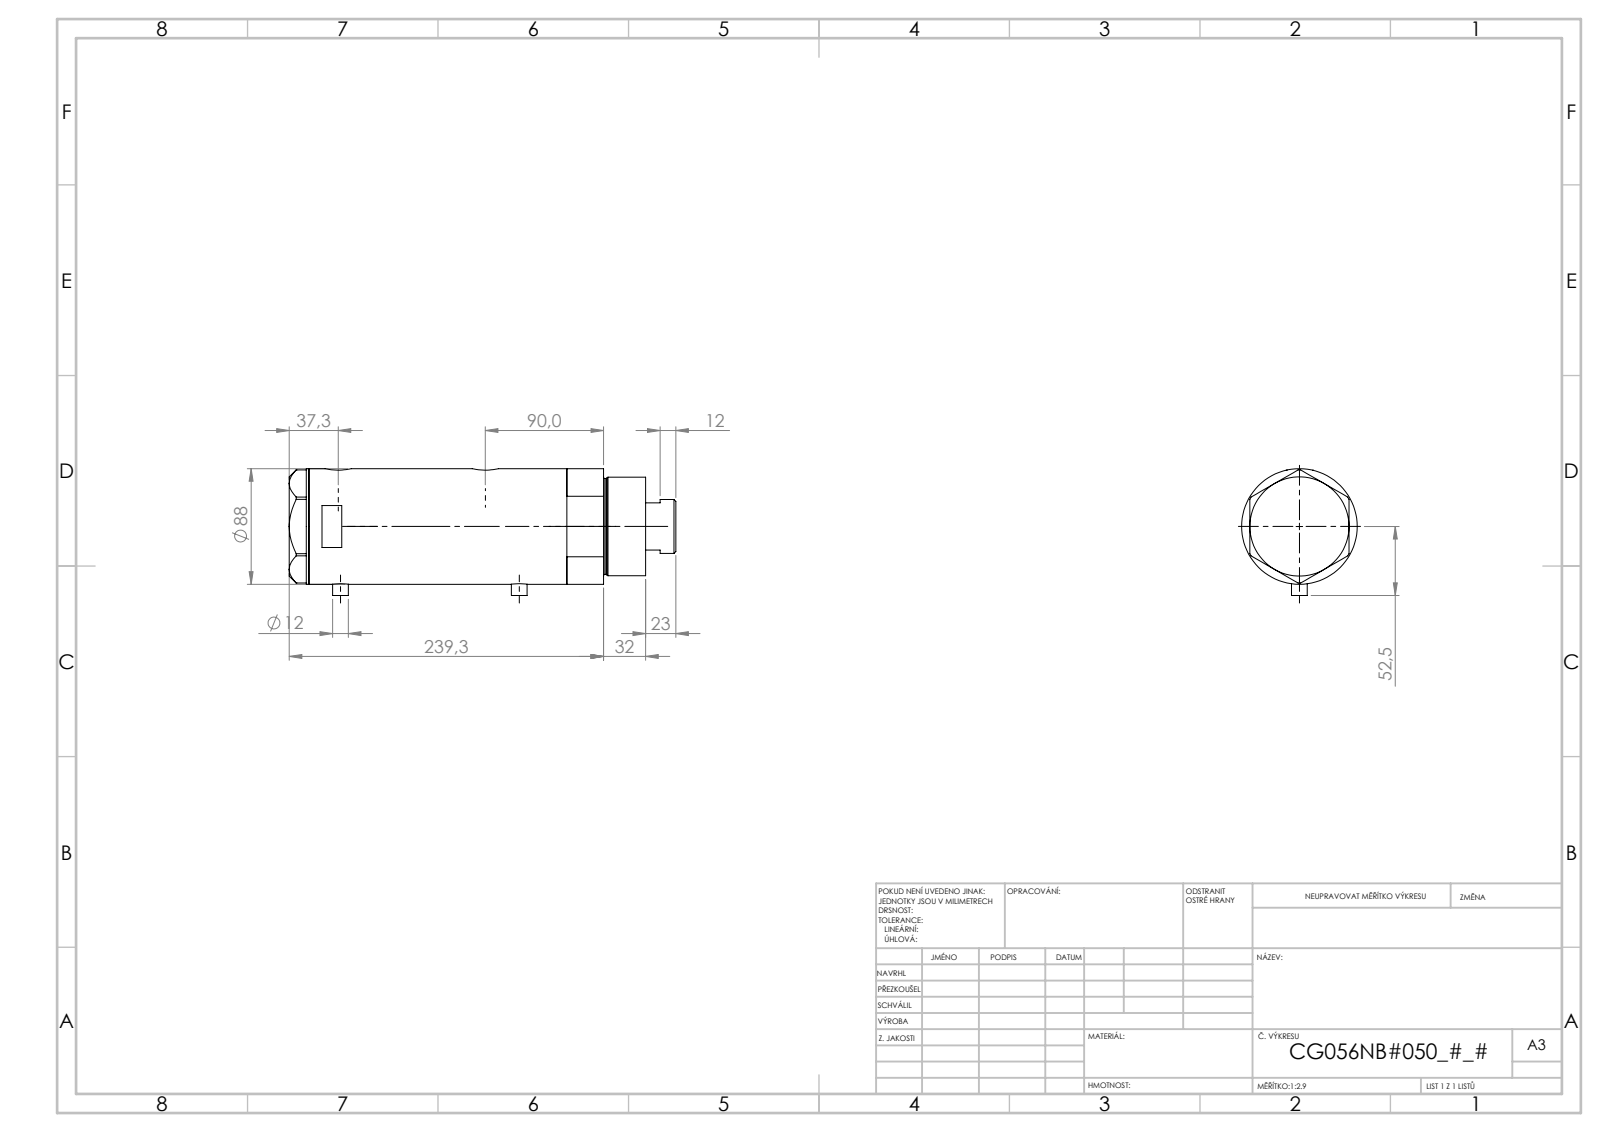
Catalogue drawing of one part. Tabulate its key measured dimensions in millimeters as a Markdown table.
| quantity | value |
| --- | --- |
| part name | V270CG_BACK; V270CG_FRONT; V270CG_VC; V270CG_MIDDLE |
| STEP written by | SolidWorks 2019 (CONFIG_CONTROL_DESIGN) |
| units | millimeters |
| bodies | 4 solids, 126 faces (53 planar, 53 cylindrical, 20 other) |
| overall size | 274.47 × 89.1 × 88 |
| volume | 1 412 000 mm³ |
| surface area | 209 477 mm² |
| round holes (diameter × count) | 5 × 2, 12.5 × 2, 13.16 × 2, 20 × 2, 14.5 × 1, 42 × 1, 43.5 × 1, 56 × 1, 60 × 1, 80 × 1 |
| round bosses / shafts (diameter × count) | 12 × 2, 88 × 1, 75 × 1, 73 × 1, 41 × 1 |
| main face-to-face distances | 124.4, 26, 98.4, 15, 41, 139.4, 236.47, 251.47, 210.47, 112.07 |
| hole center spacings | 1.7, 25.8, 100.3, 102, 126.1, 127.8 |
